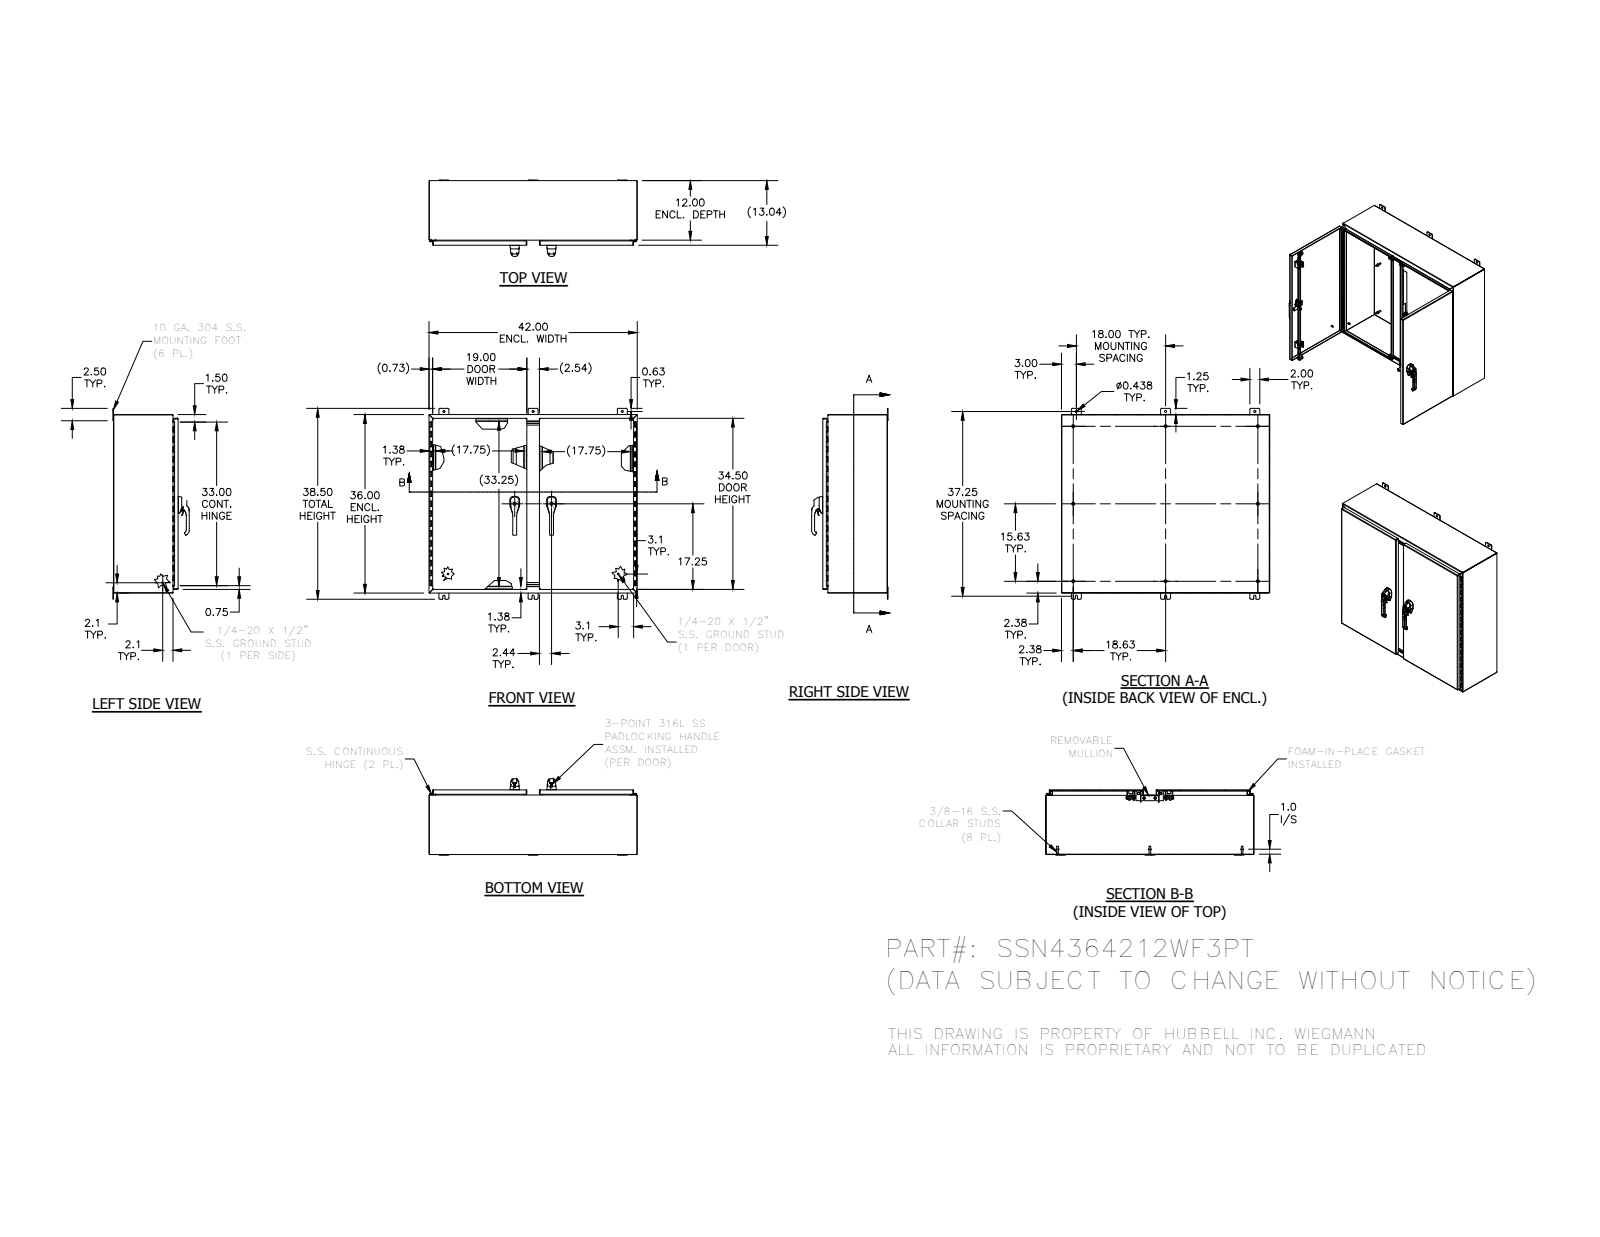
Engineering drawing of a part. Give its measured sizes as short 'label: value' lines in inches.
name: 38846; HFW303115; 2100-11; D125B_10_5 (+8 more)
written by: SolidWorks 2014 (AUTOMOTIVE_DESIGN)
unit: in
bodies: 127 solids, 6644 faces (2382 planar, 2742 cylindrical, 1520 other)
size: 42 × 38.5 × 15.409
volume: 491.9 in³; area: 12 177 in²
holes: 12× ⌀0.262, 8× ⌀0.187, 6× ⌀0.213, 6× ⌀0.28, 6× ⌀0.438, 4× ⌀0.196, 4× ⌀0.252, 4× ⌀0.281, 4× ⌀0.315, 4× ⌀0.4, 4× ⌀0.402, 4× ⌀0.45
bosses: 9× ⌀0.25, 8× ⌀0.625, 8× ⌀0.33, 6× ⌀0.533, 5× ⌀0.236, 4× ⌀0.531, 4× ⌀0.438, 4× ⌀0.435
rounds: 317× R0.02, 221× R0.012, 39× R0.019, 33× R0.031, 31× R0.125, 30× R0.05, 30× R0.25, 25× R0.079
face distances: 0.074, 0.094, 12.942, 12.868, 13.035, 12.961, 35.926, 41.926, 11.926, 35.852
hole spacings: 0.38, 0.76, 7.417, 0.492, 0.492, 0.886, 1.236, 1.376
